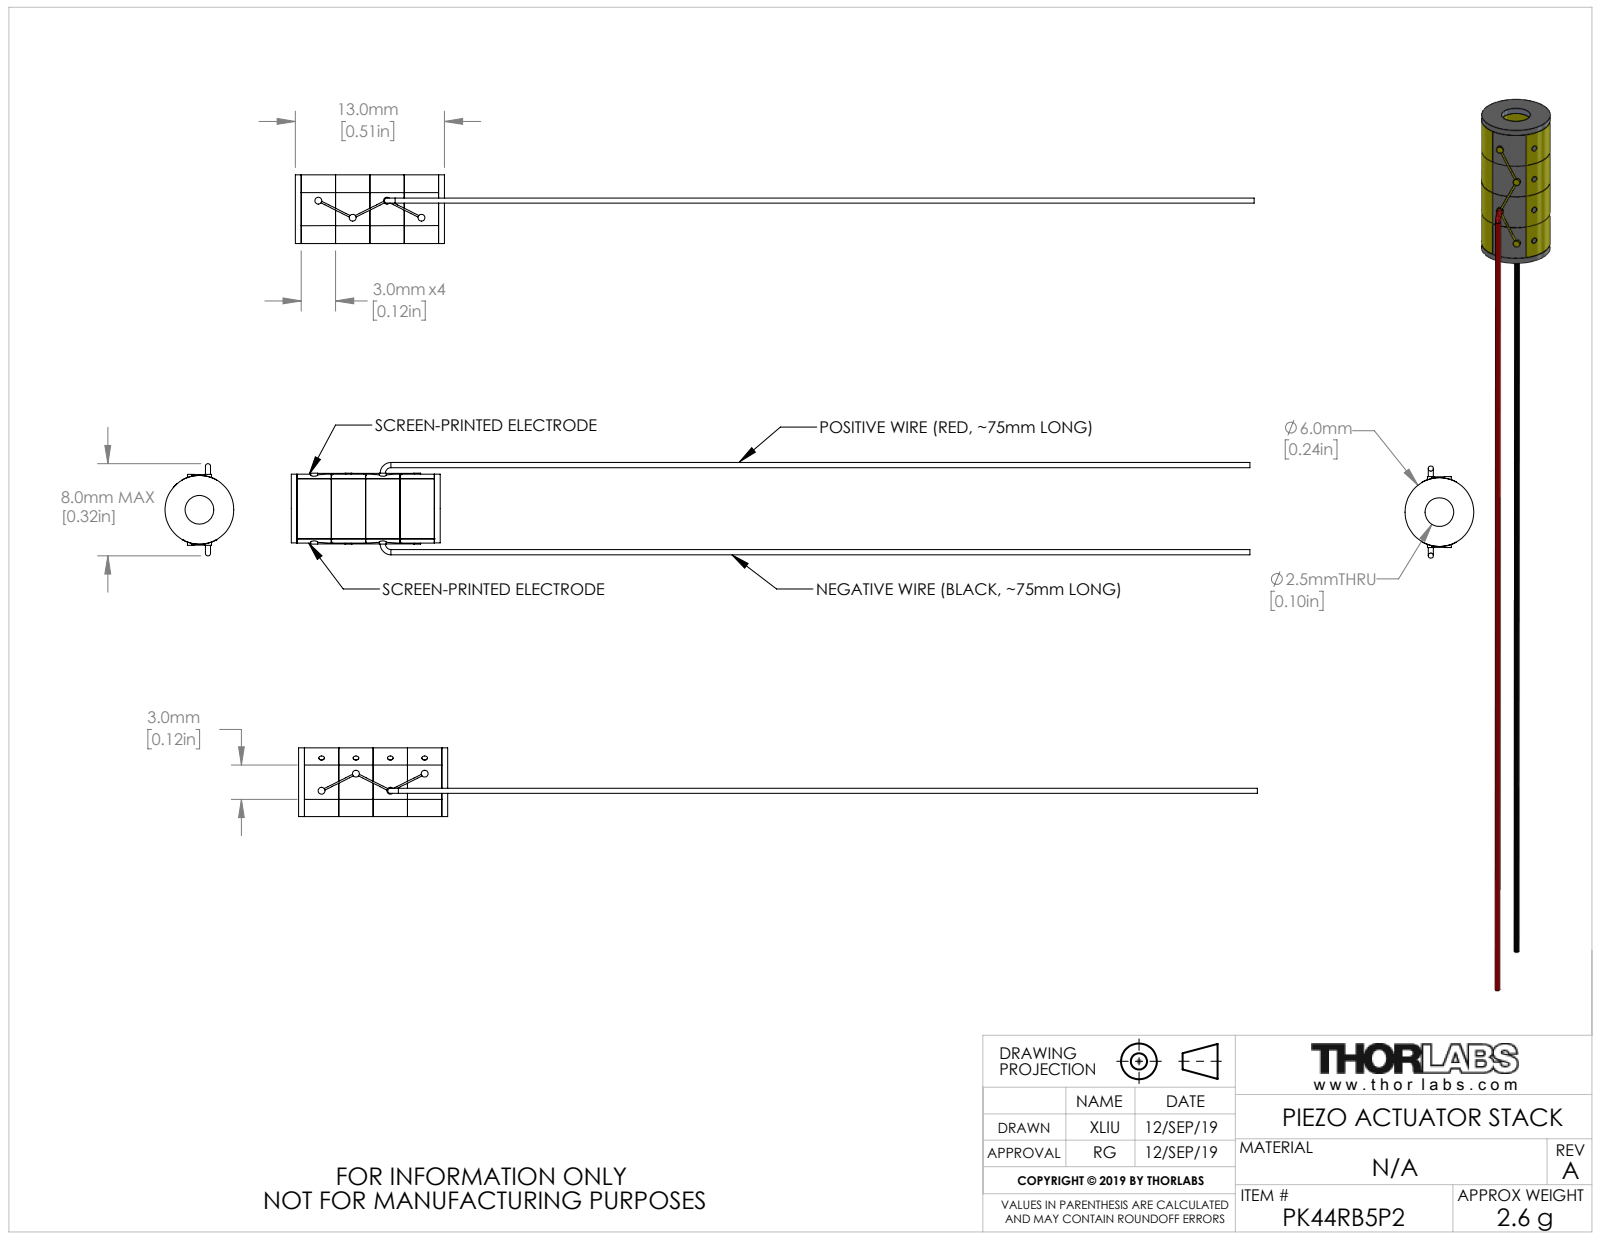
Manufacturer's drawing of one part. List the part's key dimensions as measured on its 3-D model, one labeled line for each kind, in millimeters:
Part name (STEP PRODUCT): CTN014428
STEP written by: SolidWorks 2018 (AUTOMOTIVE_DESIGN)
Units: millimetres
Bodies: 3 solids, 150 faces (34 planar, 100 cylindrical, 16 other)
Overall size (bounding box): 83.7 × 8.05 × 6
Volume: 329 mm³ · Surface area: 848 mm²
Round holes (diameter × count): ⌀2.5 ×1
Round bosses / shafts (diameter × count): ⌀0.6 ×4, ⌀0.45 ×2, ⌀6 ×1
Partial cylindrical surfaces — rounded edges, fillets, slot ends (radius × count): R3.01 ×1
Main face-to-face distances: 3, 6, 9, 12, 0.5, 3.5, 6.5, 9.5, 12.5, 13
